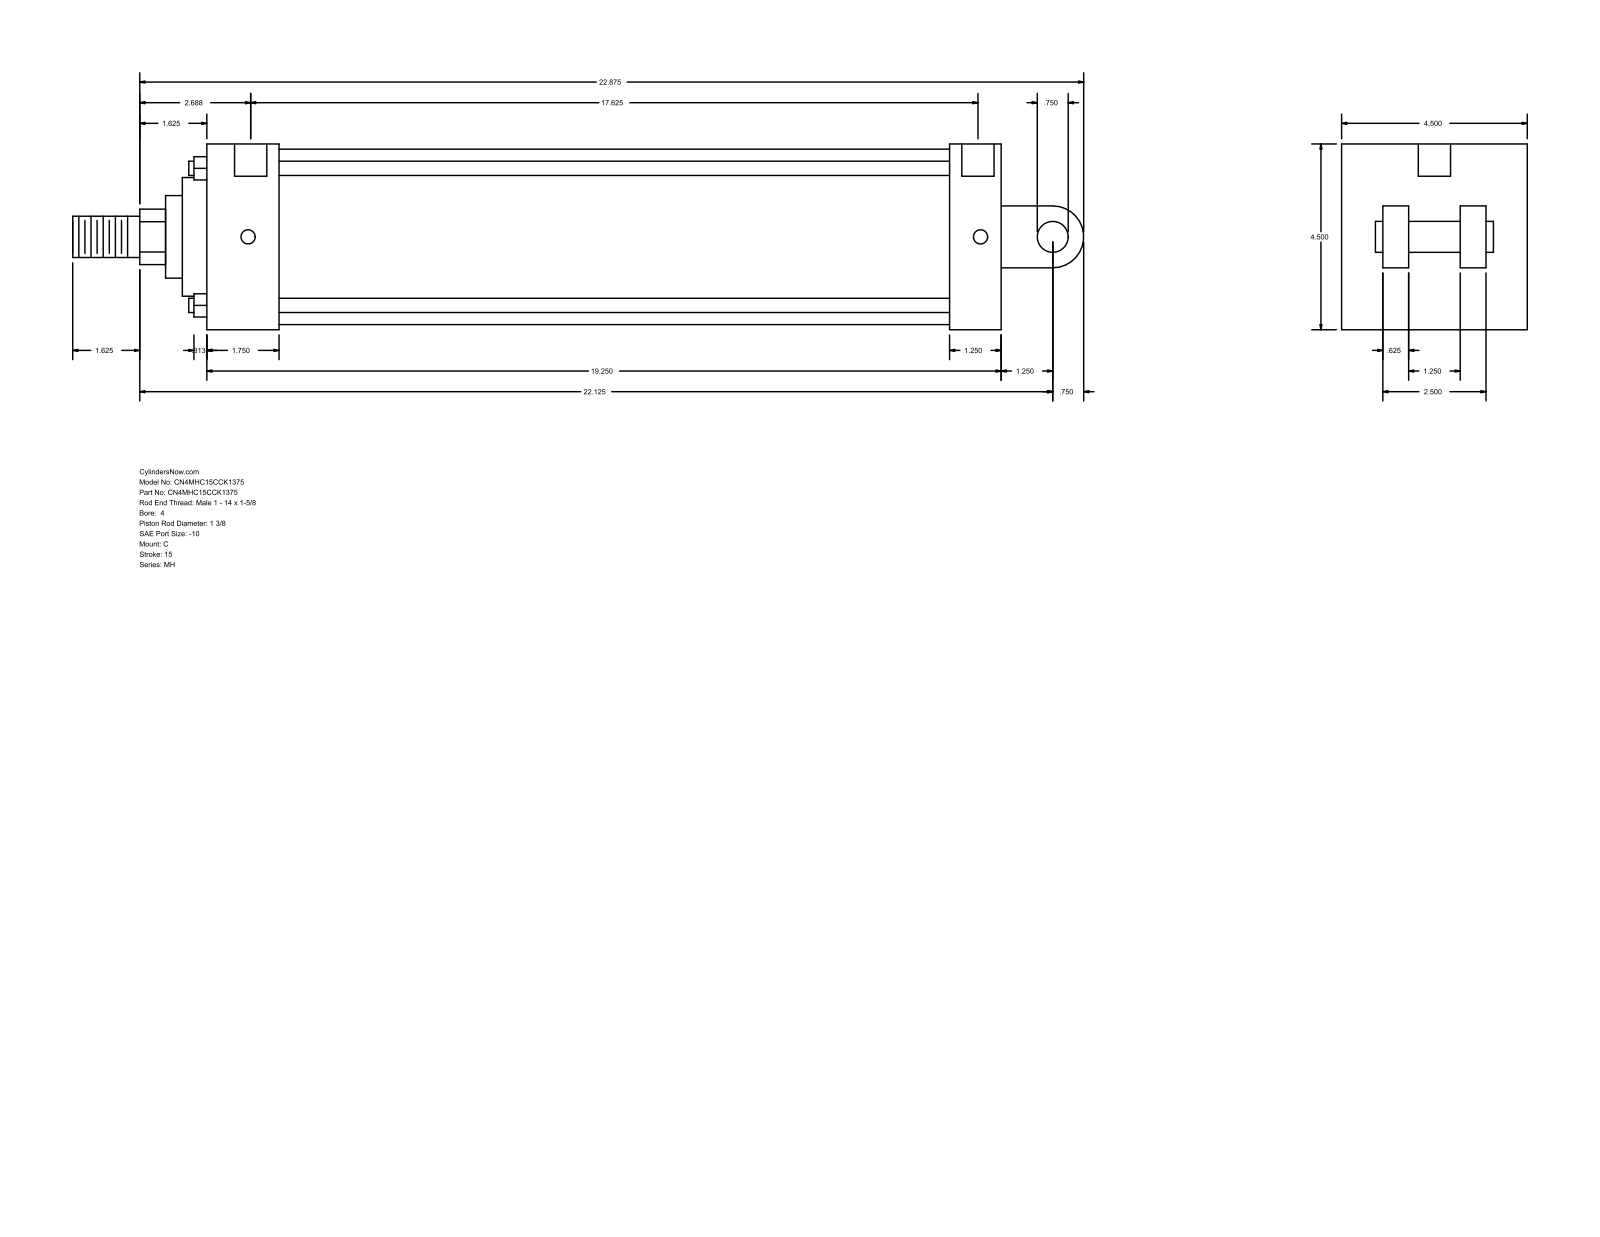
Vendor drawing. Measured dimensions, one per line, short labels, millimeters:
name: MH_C__0400_1.375
written by: GSSL Pune (CONFIG_CONTROL_DESIGN)
unit: mm
bodies: 0 solids, 101 faces (71 planar, 30 cylindrical, 0 other)
size: 622.3 × 114.3 × 114.3
holes: 4× ⌀8.73, 2× ⌀19.84
bosses: 4× ⌀8.76, 1× ⌀107.95, 1× ⌀73.03, 1× ⌀50.8, 1× ⌀34.92, 1× ⌀25.4, 1× ⌀19.05
rounds: 1× R17.06, 1× R19.05
face distances: 114.3, 488.96, 44.45, 457.21, 412.76, 444.51, 31.75, 41.27, 73.03, 38.1
hole spacings: 450.85, 1.58, 1.59, 447.68, 449.26, 449.27
